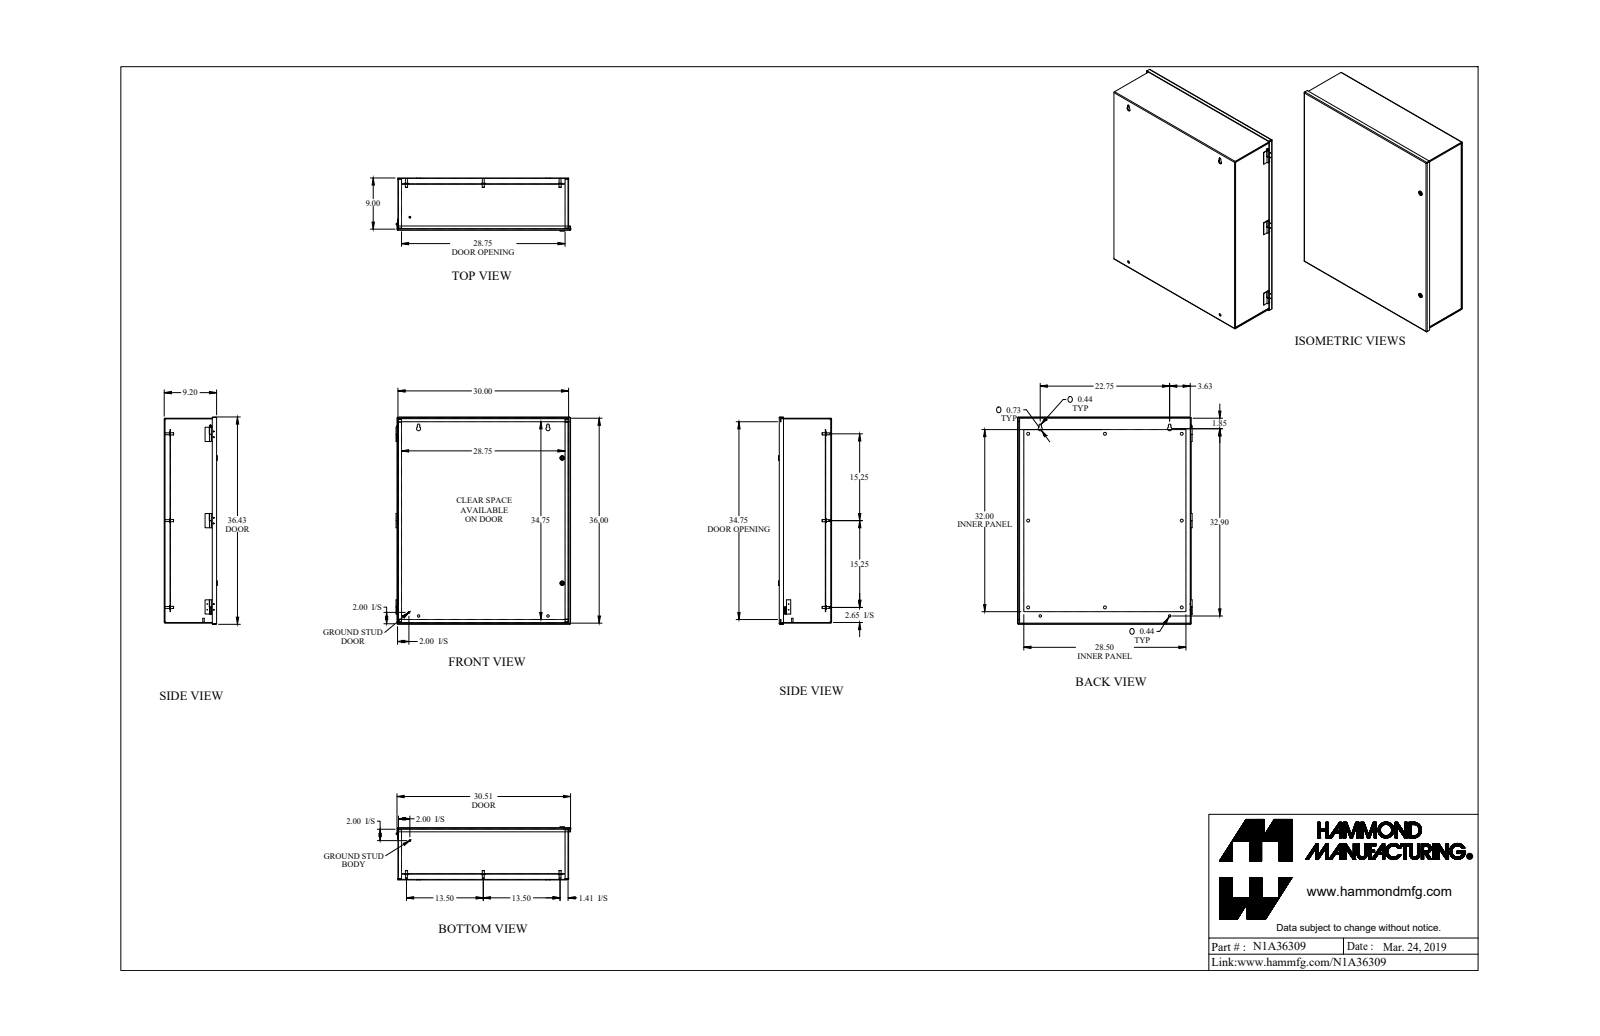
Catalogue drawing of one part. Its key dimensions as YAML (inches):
part_name: "N1A36309"
step_written_by: "SolidWorks 2018 (AUTOMOTIVE_DESIGN)"
units: inches
bodies: {solids: 36, faces: 807, planar: 442, cylindrical: 285, other: 80}
overall_size: [36.43, 30.681, 9.322]
volume: 408.1
surface_area: 9092
round_holes:
  - {diameter: 0.14, count: 12}
  - {diameter: 0.5, count: 8}
  - {diameter: 0.307, count: 4}
  - {diameter: 0.445, count: 4}
  - {diameter: 0.734, count: 3}
  - {diameter: 0.437, count: 2}
  - {diameter: 0.516, count: 2}
  - {diameter: 0.17, count: 1}
  - {diameter: 0.187, count: 1}
round_bosses_or_shafts:
  - {diameter: 0.128, count: 12}
  - {diameter: 0.375, count: 9}
  - {diameter: 0.65, count: 8}
  - {diameter: 0.33, count: 8}
  - {diameter: 1, count: 4}
  - {diameter: 0.788, count: 2}
  - {diameter: 0.535, count: 2}
  - {diameter: 0.496, count: 2}
partial_cylinders:
  - {radius: 0.048, count: 16}
  - {radius: 0.143, count: 16}
  - {radius: 0.219, count: 3}
  - {radius: 0.06, count: 2}
  - {radius: 0.125, count: 2}
  - {radius: 0.153, count: 2}
  - {radius: 0.315, count: 2}
  - {radius: 0.03, count: 1}
face_to_face_distances: [0.095, 0.095, 9.01, 9.105, 9.105, 9.2, 0.072, 0.937, 1.104, 1.009]
hole_center_spacings: [1, 1.119, 13.5, 15.25, 20.367, 30.335, 31.009, 33.354]
